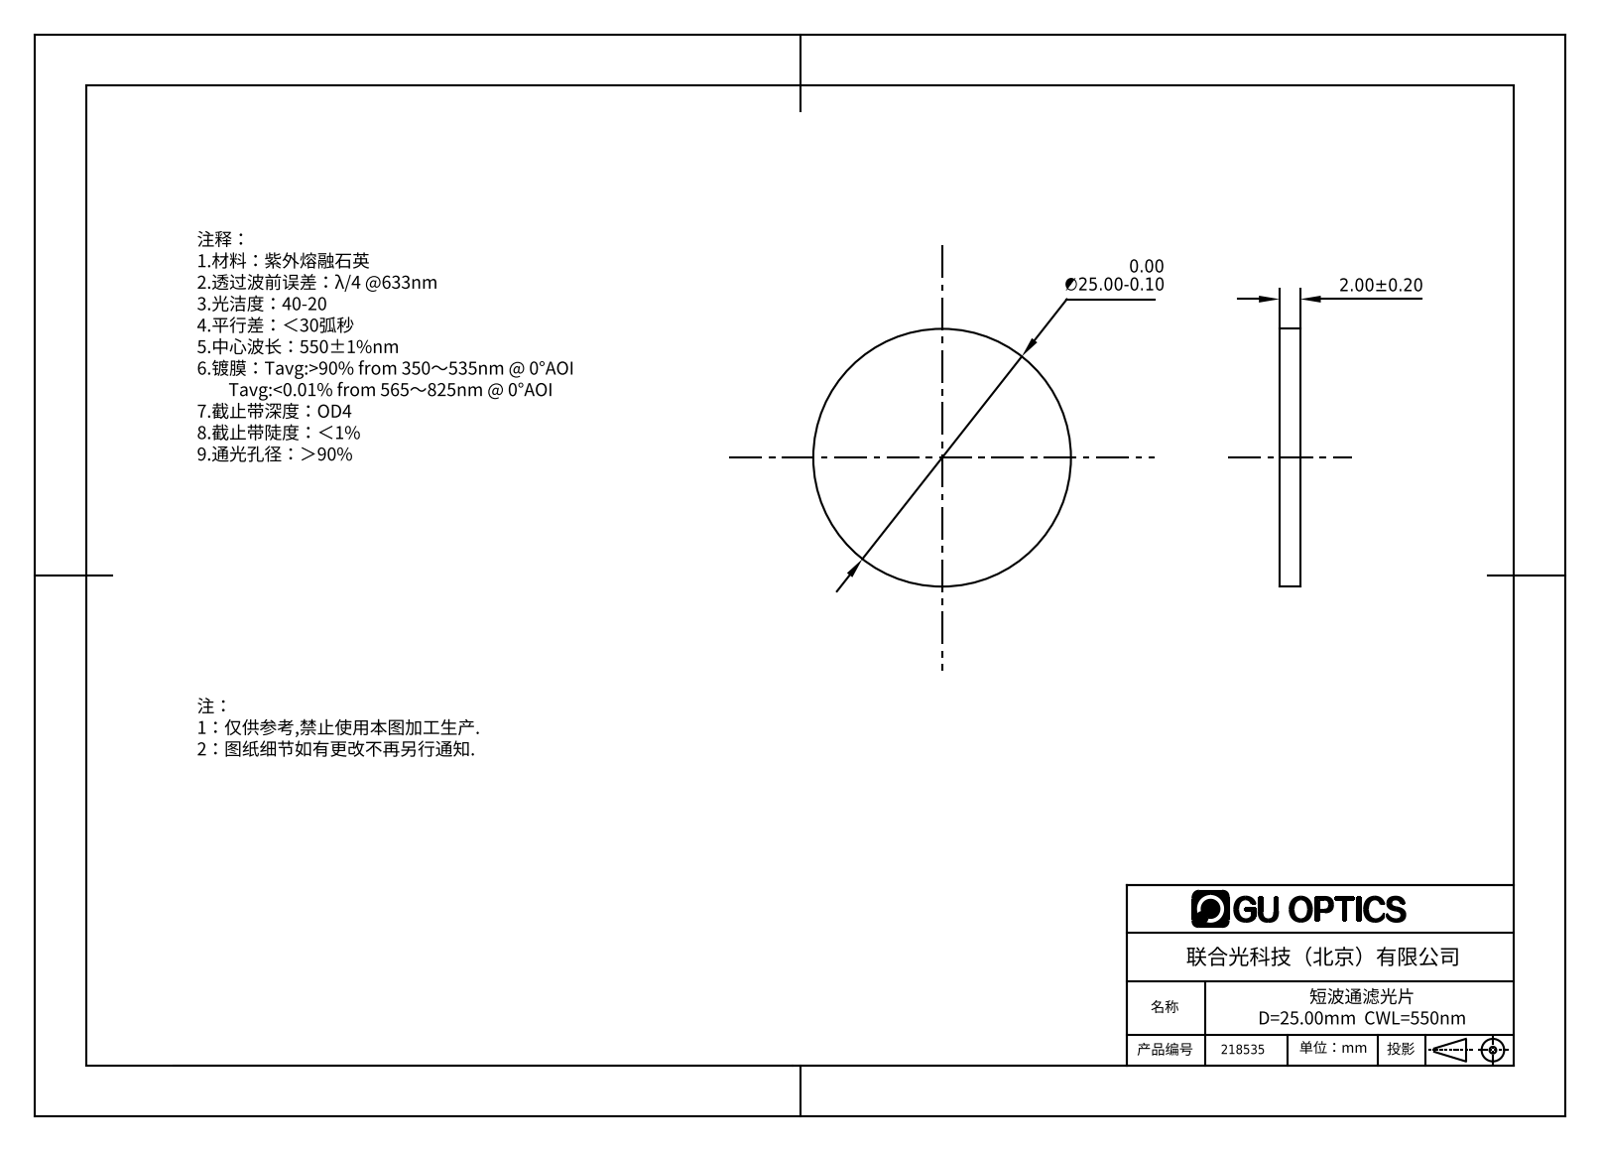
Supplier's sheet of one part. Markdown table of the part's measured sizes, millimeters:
| quantity | value |
| --- | --- |
| part name | 218529 |
| STEP written by | SolidWorks 2016 (AUTOMOTIVE_DESIGN) |
| units | millimeters |
| bodies | 1 solid, 4 faces (2 planar, 2 cylindrical, 0 other) |
| overall size | 25 × 25 × 2 |
| volume | 982 mm³ |
| surface area | 1 139 mm² |
| round bosses / shafts (diameter × count) | 25 × 1 |
| main face-to-face distances | 2 |
